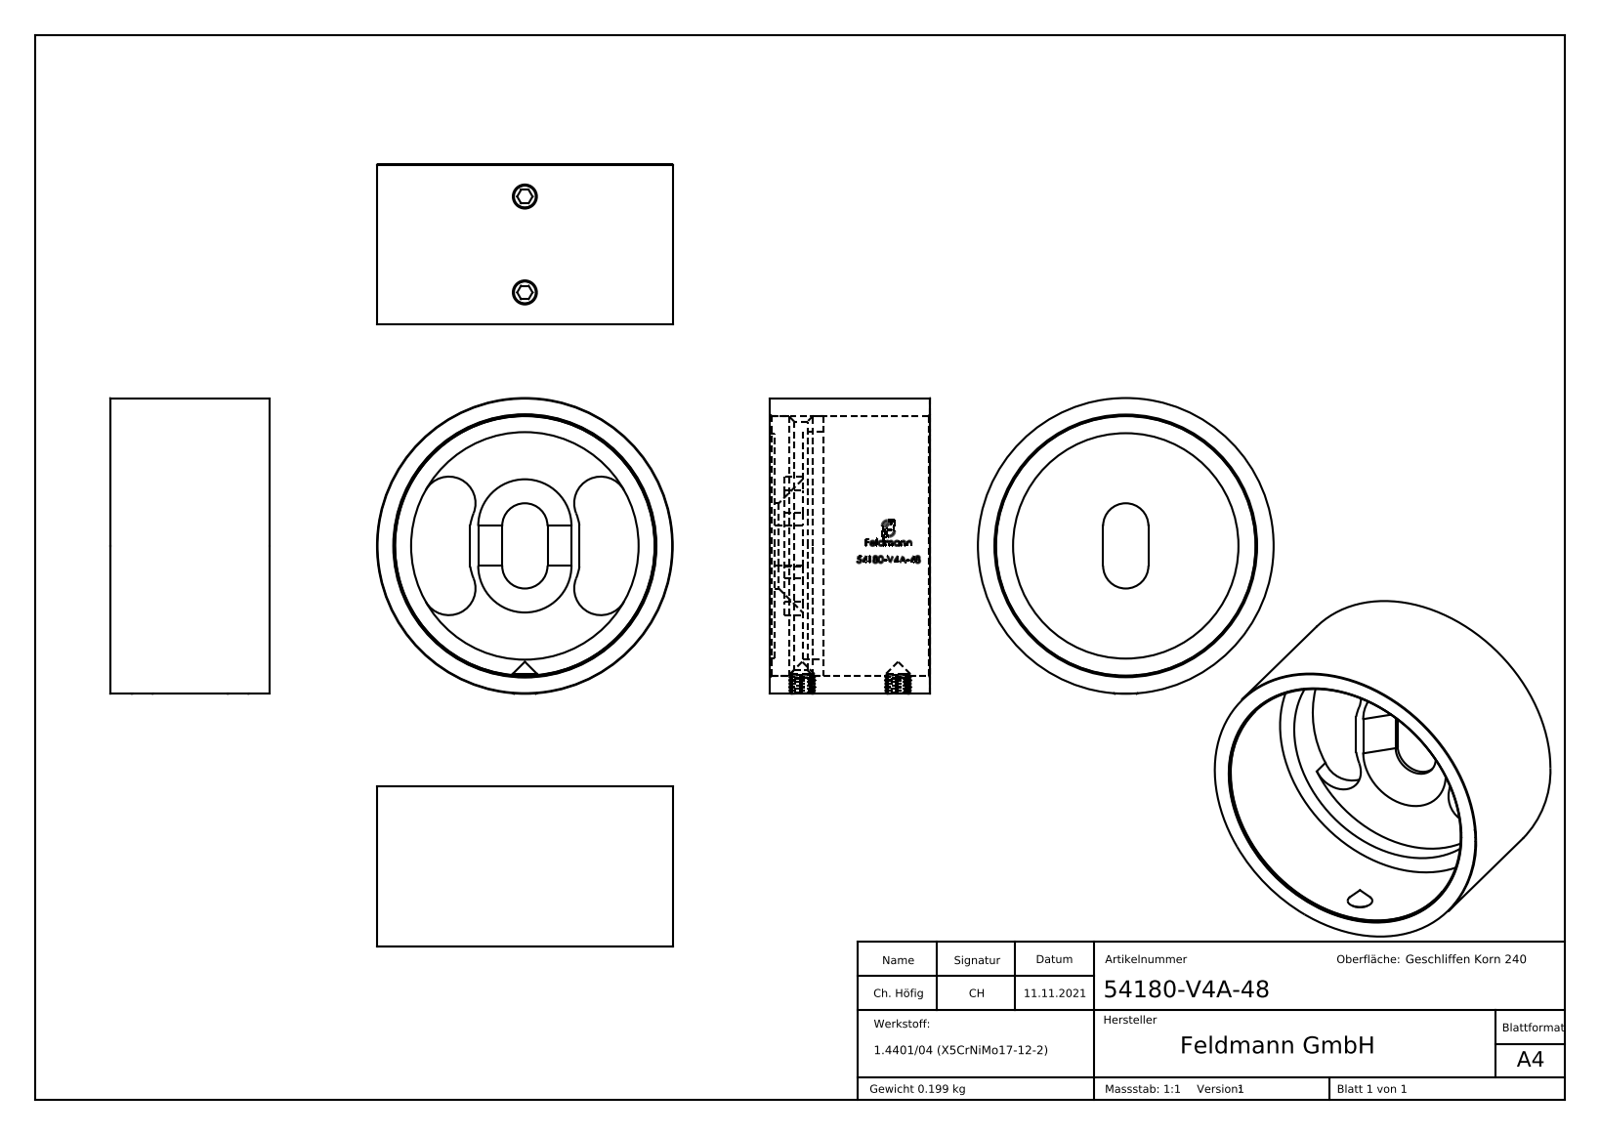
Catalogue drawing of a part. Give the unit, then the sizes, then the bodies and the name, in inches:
Units: inches
Overall size (bounding box): 2.185 × 2.185 × 1.181
Round holes (diameter × count): ⌀0.165 ×2, ⌀1.665 ×1, ⌀1.681 ×1, ⌀1.921 ×1
Round bosses / shafts (diameter × count): ⌀0.197 ×2, ⌀2.185 ×1, ⌀1.917 ×1, ⌀1.839 ×1
Partial cylindrical surfaces — rounded edges, fillets, slot ends (radius × count): R0.197 ×4, R0.167 ×2, R0.409 ×2, R0.961 ×1
Main face-to-face distances: 0.031, 0.24, 0.209, 0.102, 0.071, 0.138, 1.181, 1.15, 1.079, 0.941
Hole centre spacings: 0.709
Volume: 1.522 in³ · Surface area: 27.22 in²
Bodies: 4 solids, 403 faces (185 planar, 62 cylindrical, 156 other)
Part name (STEP PRODUCT): 54180-240-XX Teil1_54180-V4A-48 Teil1; 54180-240-XX Teil1; 54180-V4A-48; socket set screw cone point_din_DIN 914 - M5 x 6-S (+3 more)
STEP written by: SolidWorks 2018 (CONFIG_CONTROL_DESIGN)
